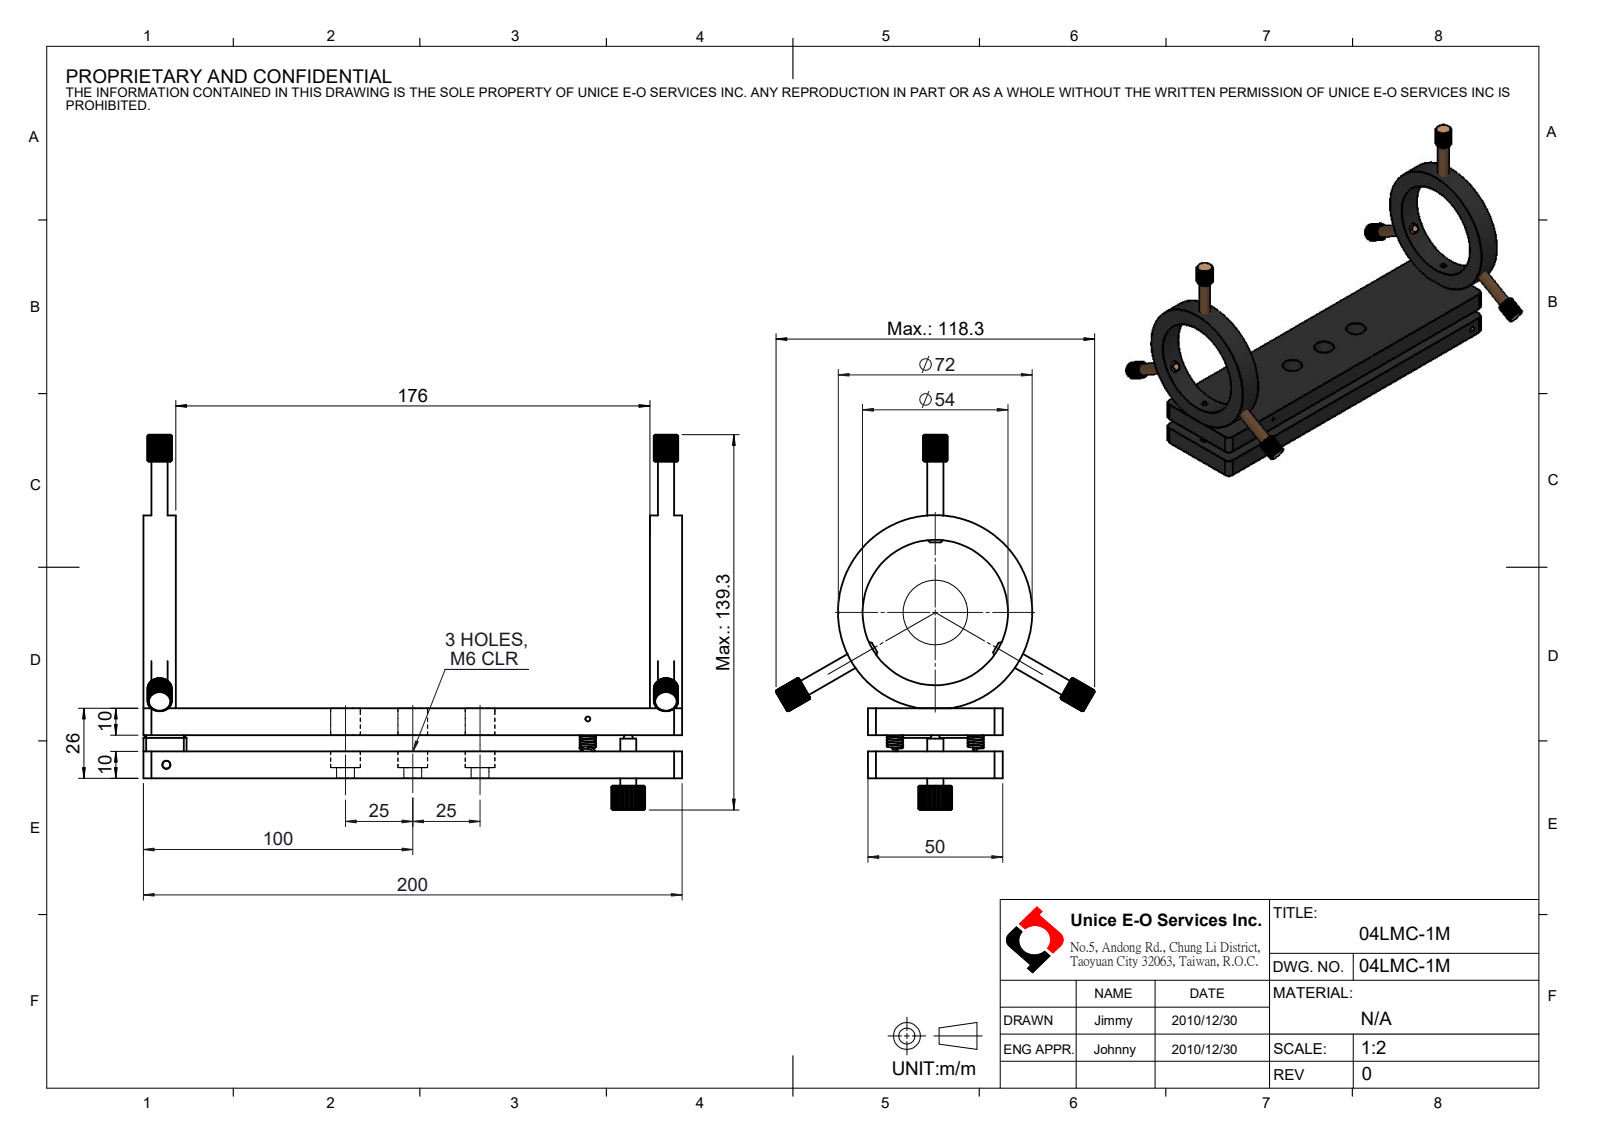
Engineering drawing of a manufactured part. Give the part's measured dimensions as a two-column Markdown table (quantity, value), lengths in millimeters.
| quantity | value |
| --- | --- |
| part name | 04LMC-1M |
| STEP written by | SolidWorks 2016 (CONFIG_CONTROL_DESIGN) |
| units | millimeters |
| bodies | 17 solids, 1213 faces (644 planar, 494 cylindrical, 75 other) |
| overall size | 200 × 139.25 × 118.31 |
| volume | 245 000 mm³ |
| surface area | 81 185 mm² |
| round holes (diameter × count) | 5 × 7, 6.6 × 3, 11 × 3, 1.25 × 2, 3.3 × 2, 4.5 × 2, 6 × 2, 8 × 2, 1.8 × 1, 3 × 1, 4.1 × 1, 54 × 1 |
| round bosses / shafts (diameter × count) | 6 × 7, 1.6 × 2, 0.8 × 2, 72 × 1 |
| partial cylindrical surfaces (radius × count) | 0.25 × 40, 3 × 8, 4.5 × 6, 1 × 4, 2 × 1, 6.25 × 1 |
| main face-to-face distances | 10, 16, 26, 6, 50, 12, 188, 200, 176, 40 |
| hole center spacings | 188, 21.21, 25, 32.65, 42.72, 66.71, 69, 91.24 |
